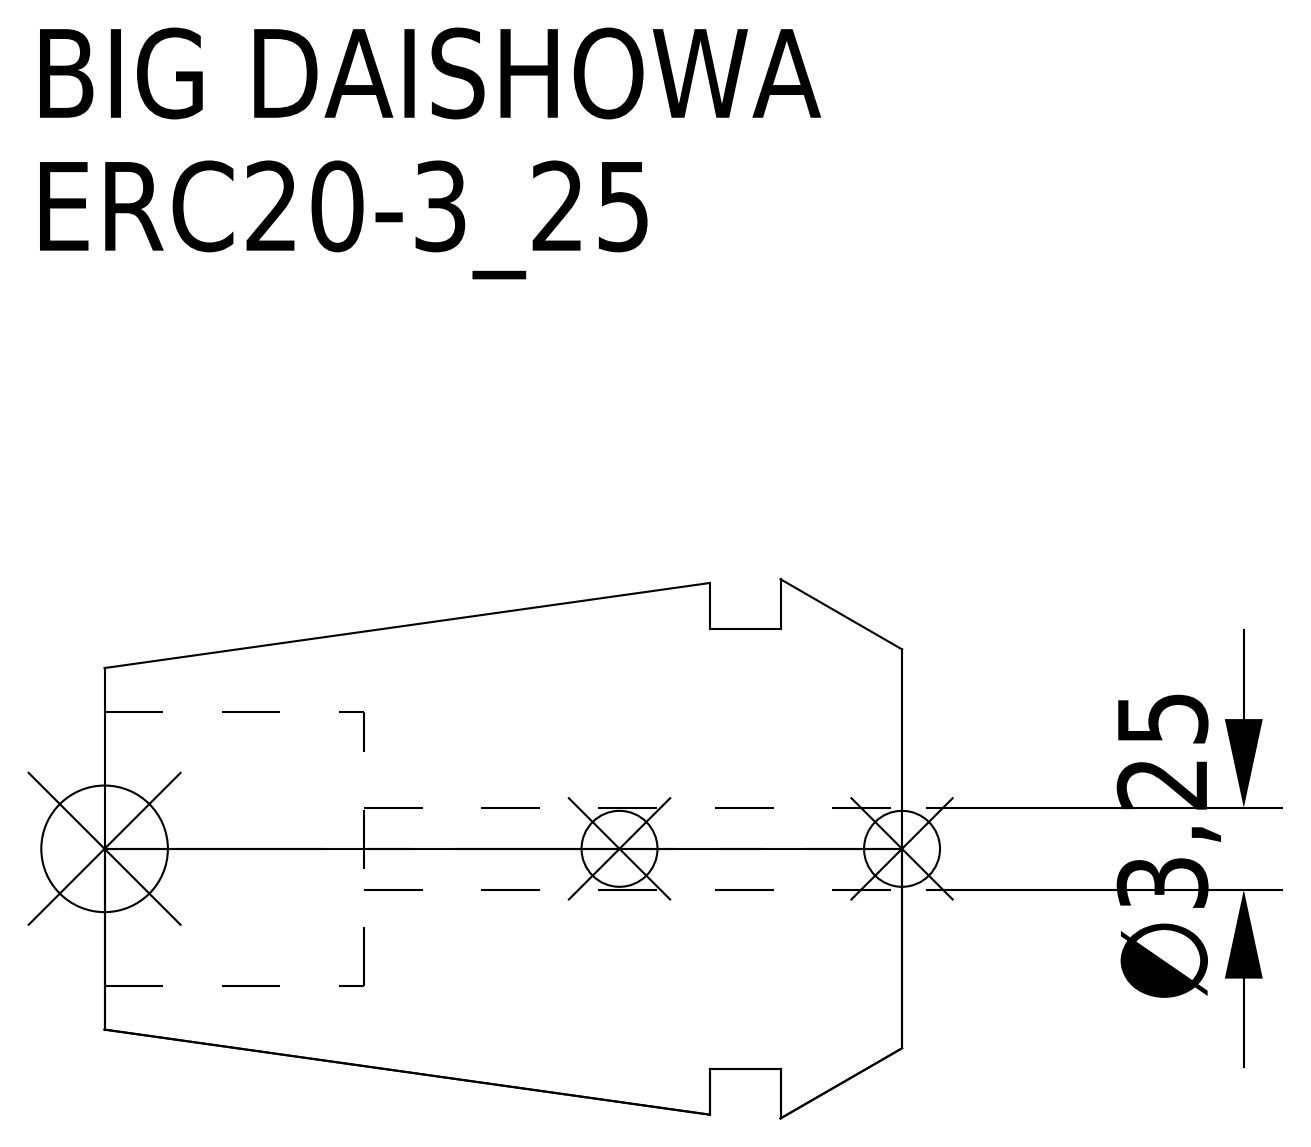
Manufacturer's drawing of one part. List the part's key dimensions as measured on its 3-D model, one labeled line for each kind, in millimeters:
Part name (STEP PRODUCT): ERC20-3_25
STEP written by: CREO PARAMETRIC BY PTC INC, 2016380 (AUTOMOTIVE_DESIGN)
Units: millimetres
Bodies: 1 solid, 15 faces (5 planar, 6 cylindrical, 4 other)
Overall size (bounding box): 31.5 × 21.3 × 21.3
Volume: 6 766 mm³ · Surface area: 2 944 mm²
Round holes (diameter × count): ⌀3.25 ×1, ⌀10.8 ×1
Round bosses / shafts (diameter × count): ⌀17.4 ×1
Main face-to-face distances: 4.8, 7.6, 2.8, 21.24, 16.44, 13.64, 31.5, 26.7, 23.9, 10.26
